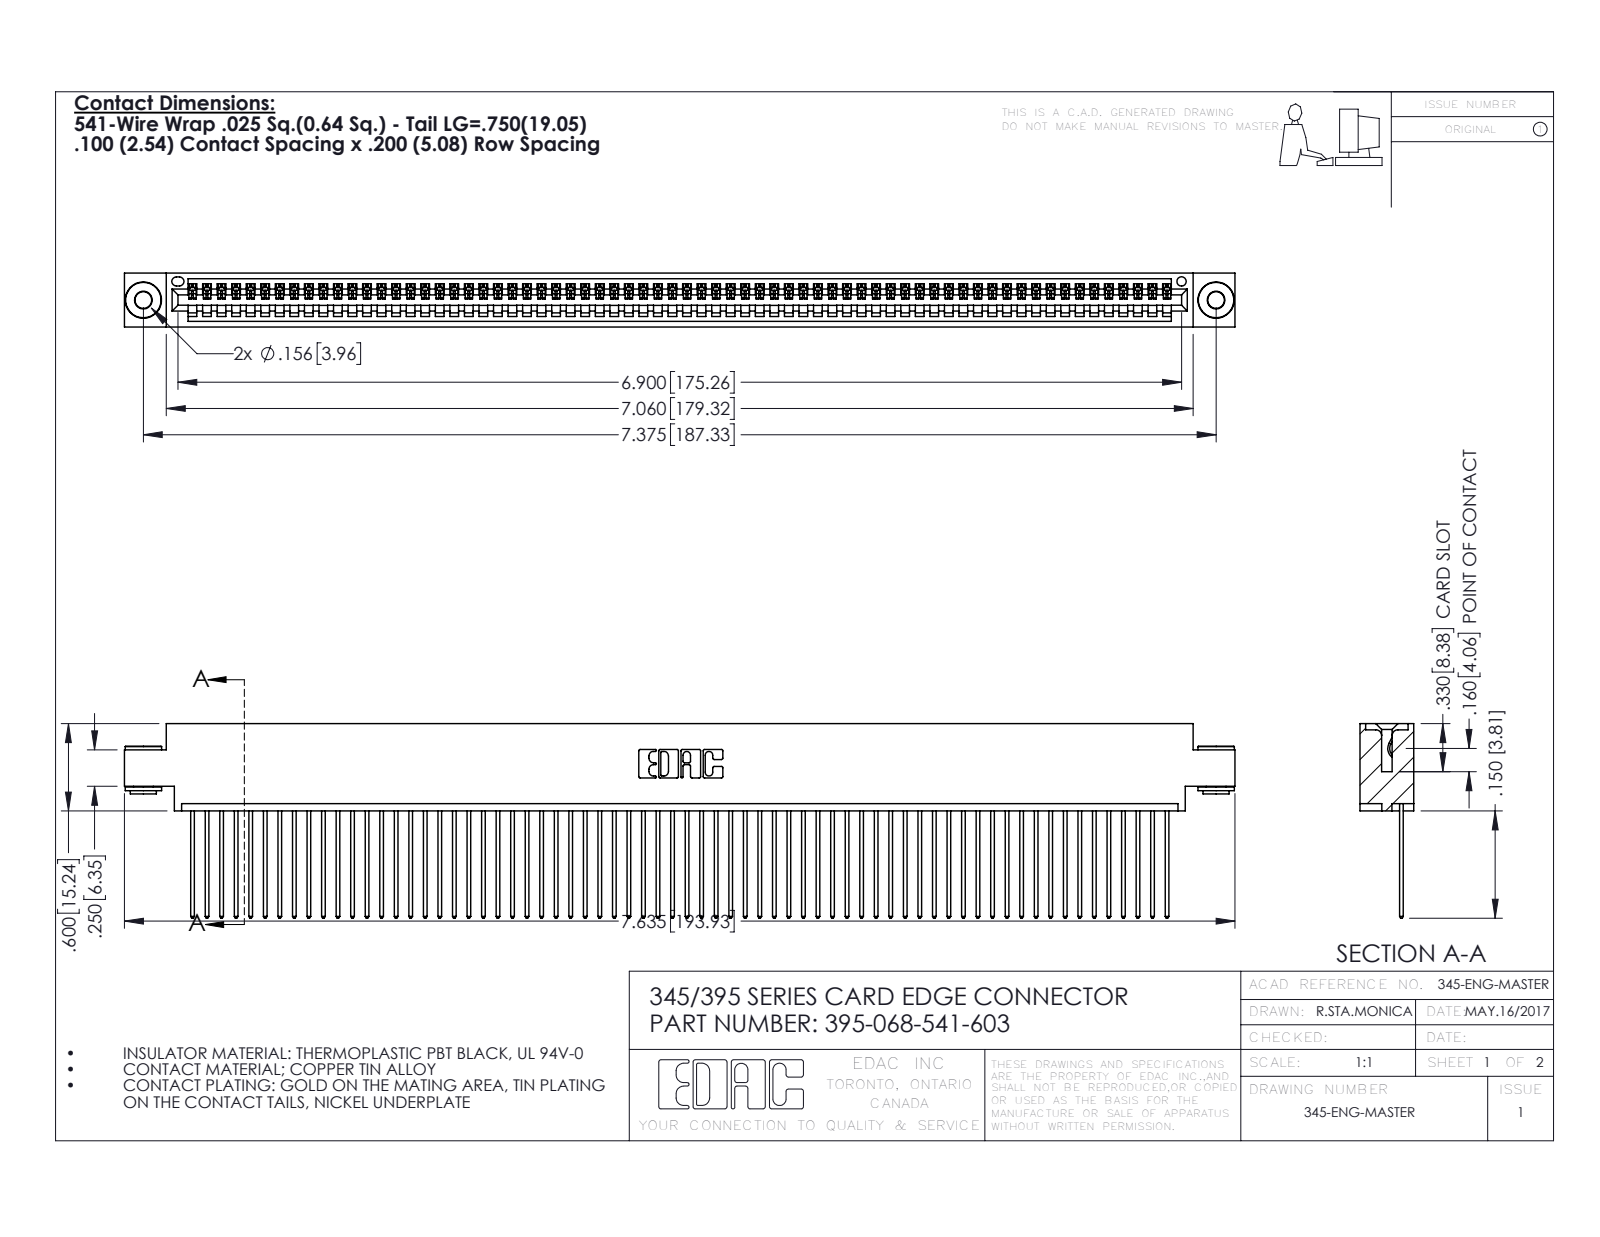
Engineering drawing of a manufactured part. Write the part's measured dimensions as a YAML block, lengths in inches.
part_name: "345-250-002_345-250-002-102; 345-292-001_345-293-141; 345 Part_0.170 Offset - 0.156 Dia-TH; 395-068-541-603"
step_written_by: "SolidWorks 2016 (CONFIG_CONTROL_DESIGN)"
units: inches
bodies: {solids: 71, faces: 4112, planar: 2814, cylindrical: 1290, other: 8}
overall_size: [7.635, 1.337, 0.37]
volume: 1.145
surface_area: 41.77
round_holes:
  - {diameter: 0.116, count: 2}
  - {diameter: 0.156, count: 2}
  - {diameter: 0.064, count: 1}
round_bosses_or_shafts:
  - {diameter: 0.25, count: 2}
  - {diameter: 0.18, count: 2}
  - {diameter: 0.136, count: 2}
partial_cylinders:
  - {radius: 0.006, count: 136}
  - {radius: 0.01, count: 136}
  - {radius: 0.01, count: 22}
  - {radius: 0.007, count: 6}
  - {radius: 0.031, count: 6}
  - {radius: 0.026, count: 3}
  - {radius: 0.031, count: 2}
  - {radius: 0.04, count: 2}
face_to_face_distances: [0.072, 0.298, 0.098, 0.272, 0.025, 0.37, 0.2, 0.225, 0.175, 0.149]
hole_center_spacings: [0.27, 7.139, 7.375]
